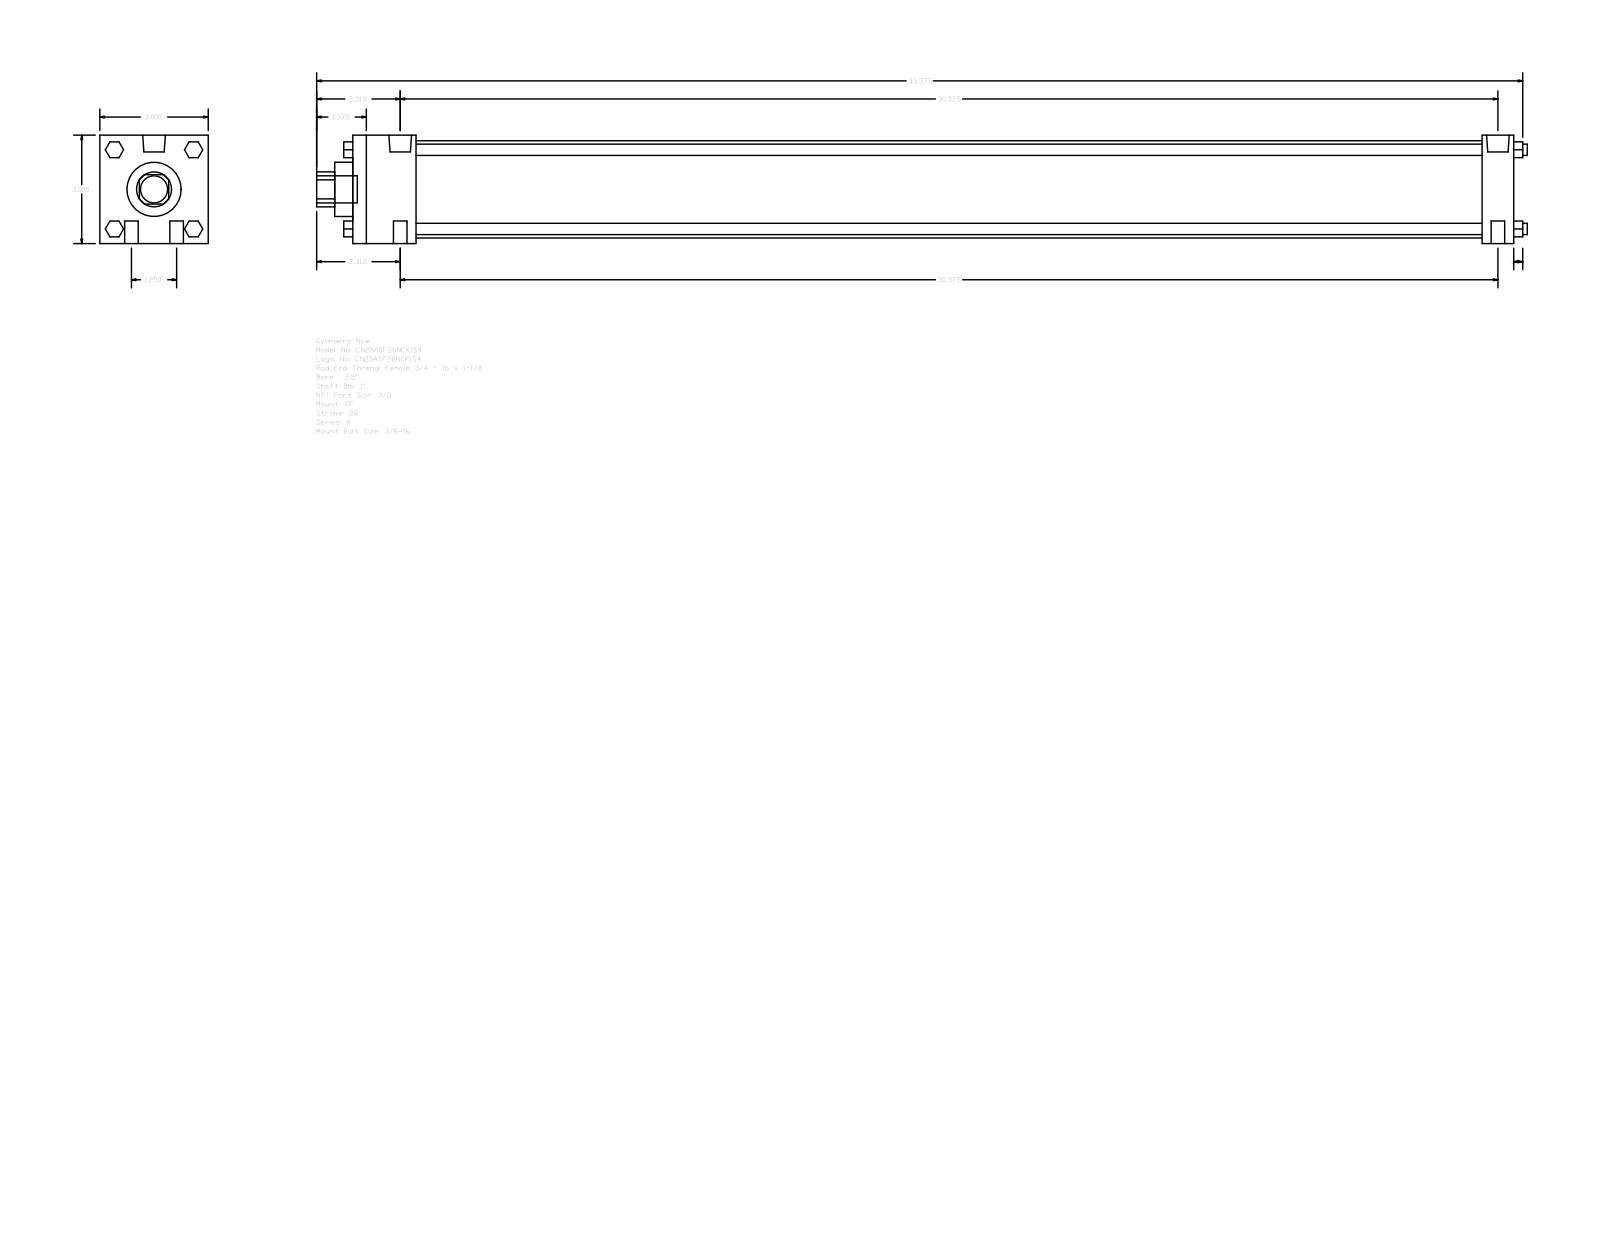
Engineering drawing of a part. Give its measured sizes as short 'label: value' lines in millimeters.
name: A_SF__0250_1
written by: GSSL Pune (CONFIG_CONTROL_DESIGN)
unit: mm
bodies: 0 solids, 124 faces (94 planar, 30 cylindrical, 0 other)
size: 850.9 × 76.2 × 76.2
holes: 1× ⌀25.4, 1× ⌀38.1, 1× ⌀68.33
bosses: 4× ⌀9.53, 4× ⌀7.94, 2× ⌀15.93, 2× ⌀5.56, 1× ⌀19.05
rounds: 1× R12.29
face distances: 76.2, 815.98, 793.75, 22.23, 44.45, 749.3, 771.53, 12.7, 828.68, 6.35
